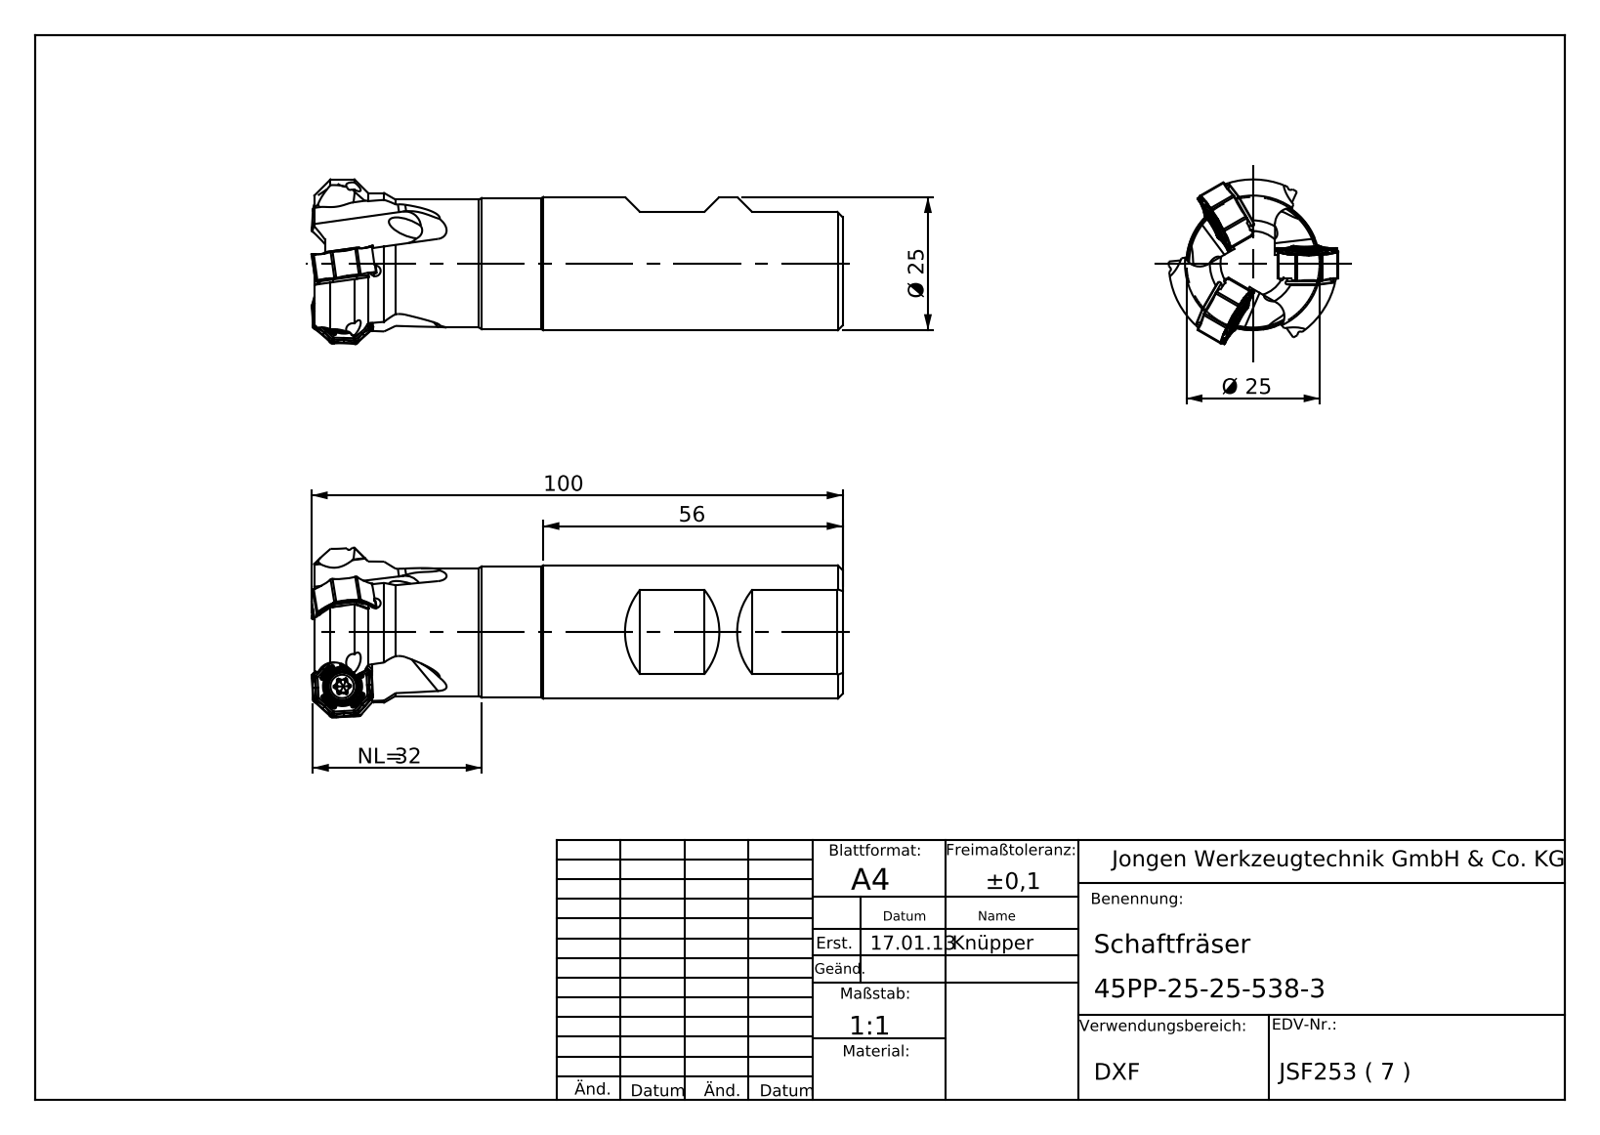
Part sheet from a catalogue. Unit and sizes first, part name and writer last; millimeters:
Units: millimetres
Overall size (bounding box): 100.07 × 32.77 × 32.77
Round holes (diameter × count): ⌀3 ×3, ⌀6.5 ×1
Round bosses / shafts (diameter × count): ⌀25 ×1, ⌀24.6 ×1, ⌀24 ×1
Partial cylindrical surfaces — rounded edges, fillets, slot ends (radius × count): R1 ×3, R1.25 ×3, R3 ×3, R13.25 ×1
Main face-to-face distances: 97.15, 14.88, 11.31, 26.19, 0.47, 1, 5.31, 5.3, 5.33, 5.99
Volume: 46 298 mm³ · Surface area: 11 477 mm²
Bodies: 1 solid, 98 faces (35 planar, 37 cylindrical, 26 other)
Part name (STEP PRODUCT): 45PP-25-25-538-3
STEP written by: SolidWorks 2013 (AUTOMOTIVE_DESIGN)
